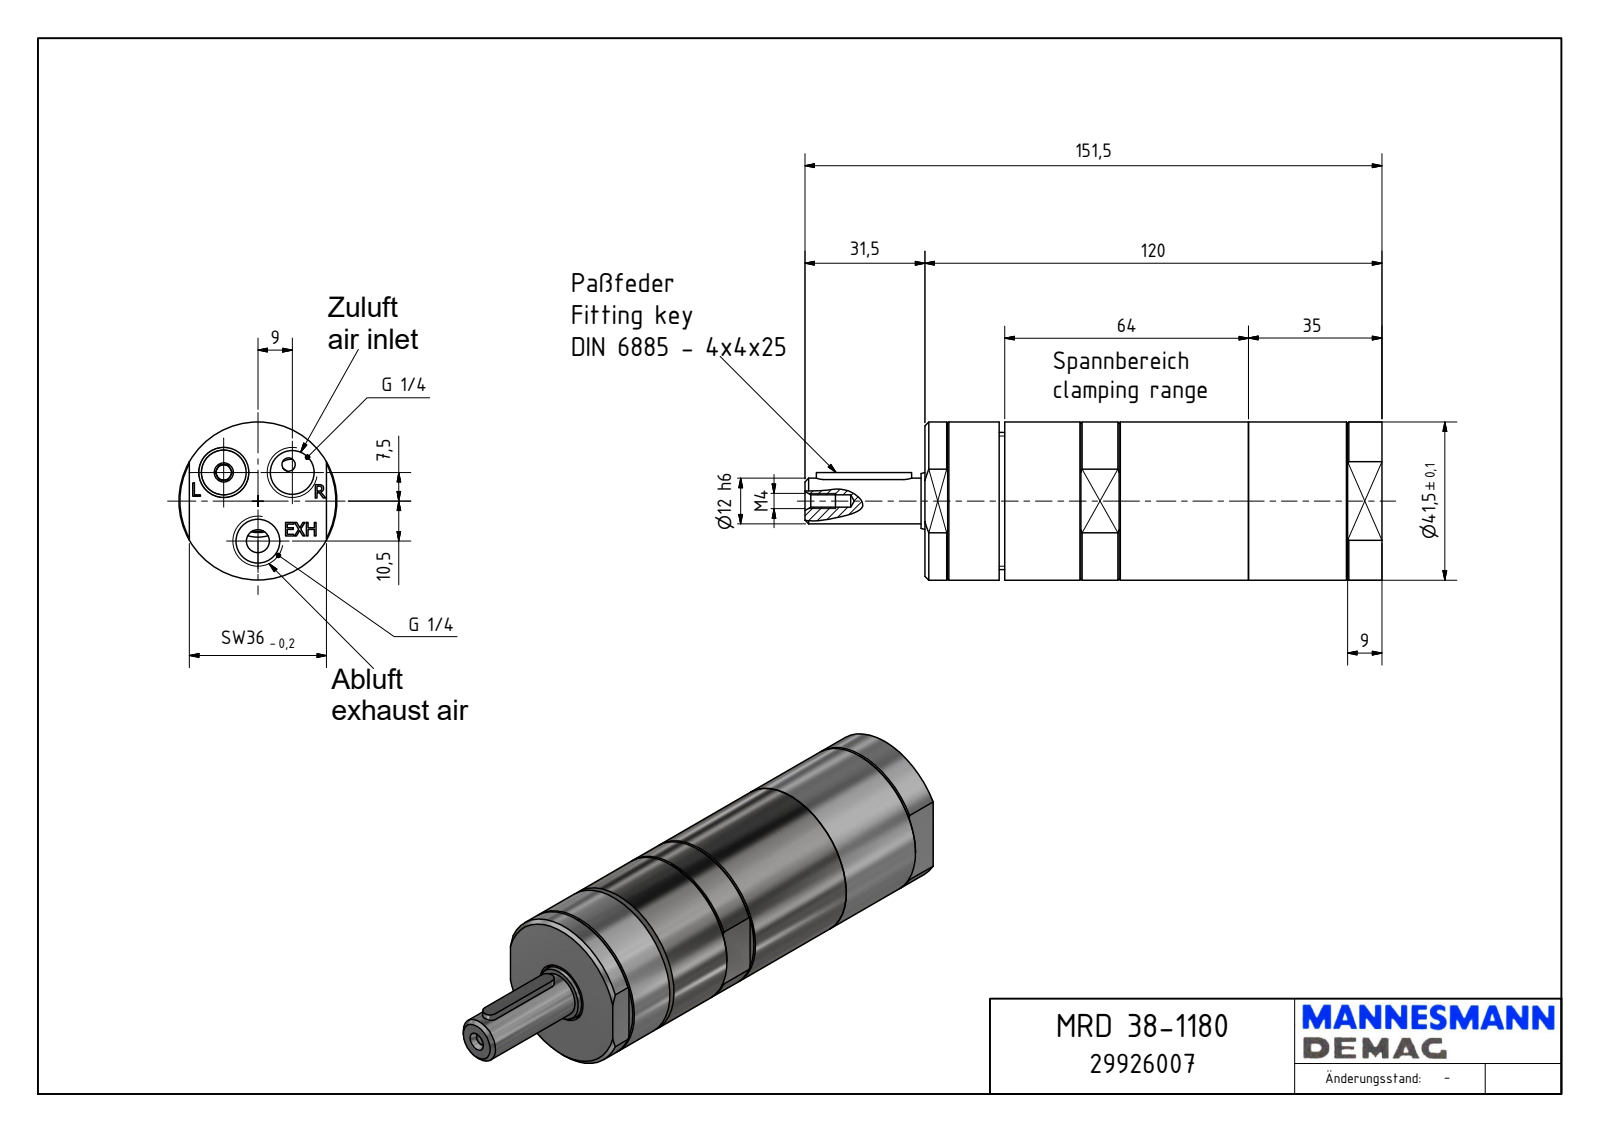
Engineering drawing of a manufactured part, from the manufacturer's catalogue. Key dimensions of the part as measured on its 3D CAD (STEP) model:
Part name (STEP PRODUCT): MRD 38-1180_29926007
STEP written by: Autodesk Inventor 2018 (AUTOMOTIVE_DESIGN)
Units: millimetres
Bodies: 1 solid, 153 faces (100 planar, 22 cylindrical, 31 other)
Overall size (bounding box): 151.5 × 41.5 × 41.5
Volume: 162 076 mm³ · Surface area: 21 244 mm²
Round holes (diameter × count): ⌀11.45 ×2, ⌀3.24 ×1, ⌀4 ×1, ⌀16 ×1
Round bosses / shafts (diameter × count): ⌀41.5 ×1, ⌀36 ×1, ⌀14.95 ×1, ⌀12 ×1
Partial cylindrical surfaces — rounded edges, fillets, slot ends (radius × count): R2 ×2, R19.49 ×1
Main face-to-face distances: 120, 1, 21, 37, 19.5, 100.5, 1.5, 99, 38, 111.15
Hole centre spacings: 11.72, 20.12, 10.5, 18
